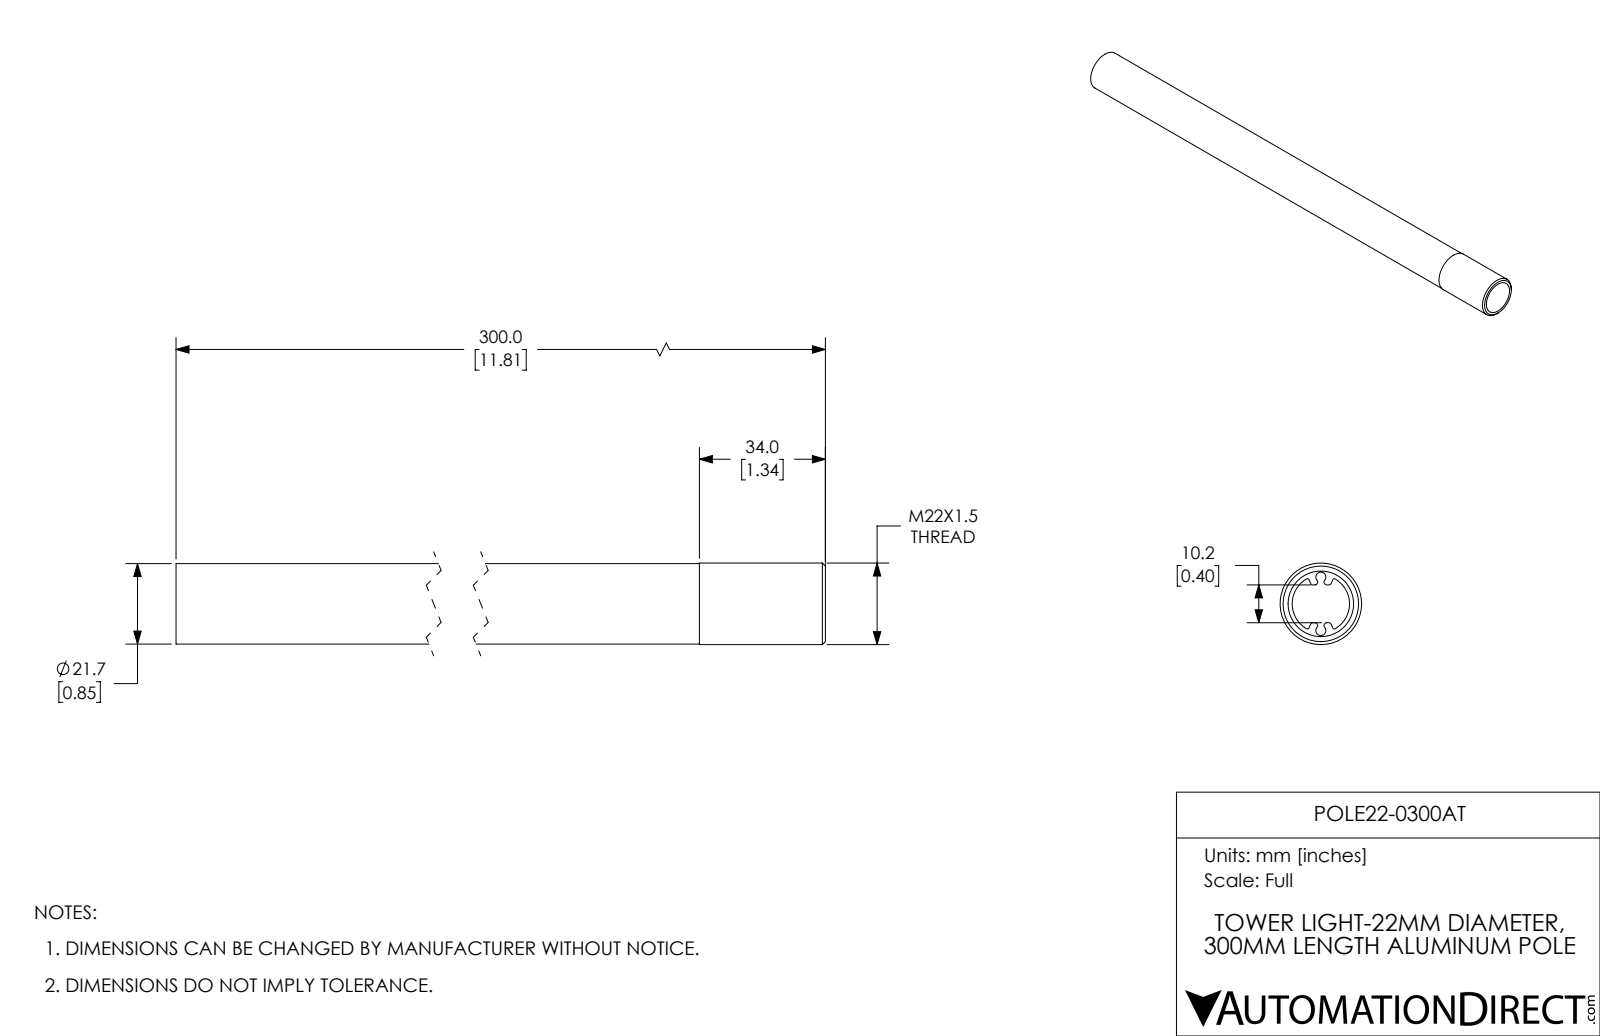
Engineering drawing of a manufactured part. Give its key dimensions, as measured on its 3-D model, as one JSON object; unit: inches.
{"part_name": "POLE22-0300AT", "step_written_by": "SolidWorks 2017 (AUTOMOTIVE_DESIGN)", "units": "inches", "bodies": {"solids": 1, "faces": 16, "planar": 4, "cylindrical": 6, "other": 6}, "overall_size": [11.811, 0.866, 0.866], "volume_in3": 3.524, "surface_area_in2": 62.15, "round_holes": [[0.697, 1]], "round_bosses_or_shafts": [[0.866, 1], [0.854, 1]], "face_to_face_distances": [11.811, 0.728, 11.083, 1.339, 0.61, 10.472]}
